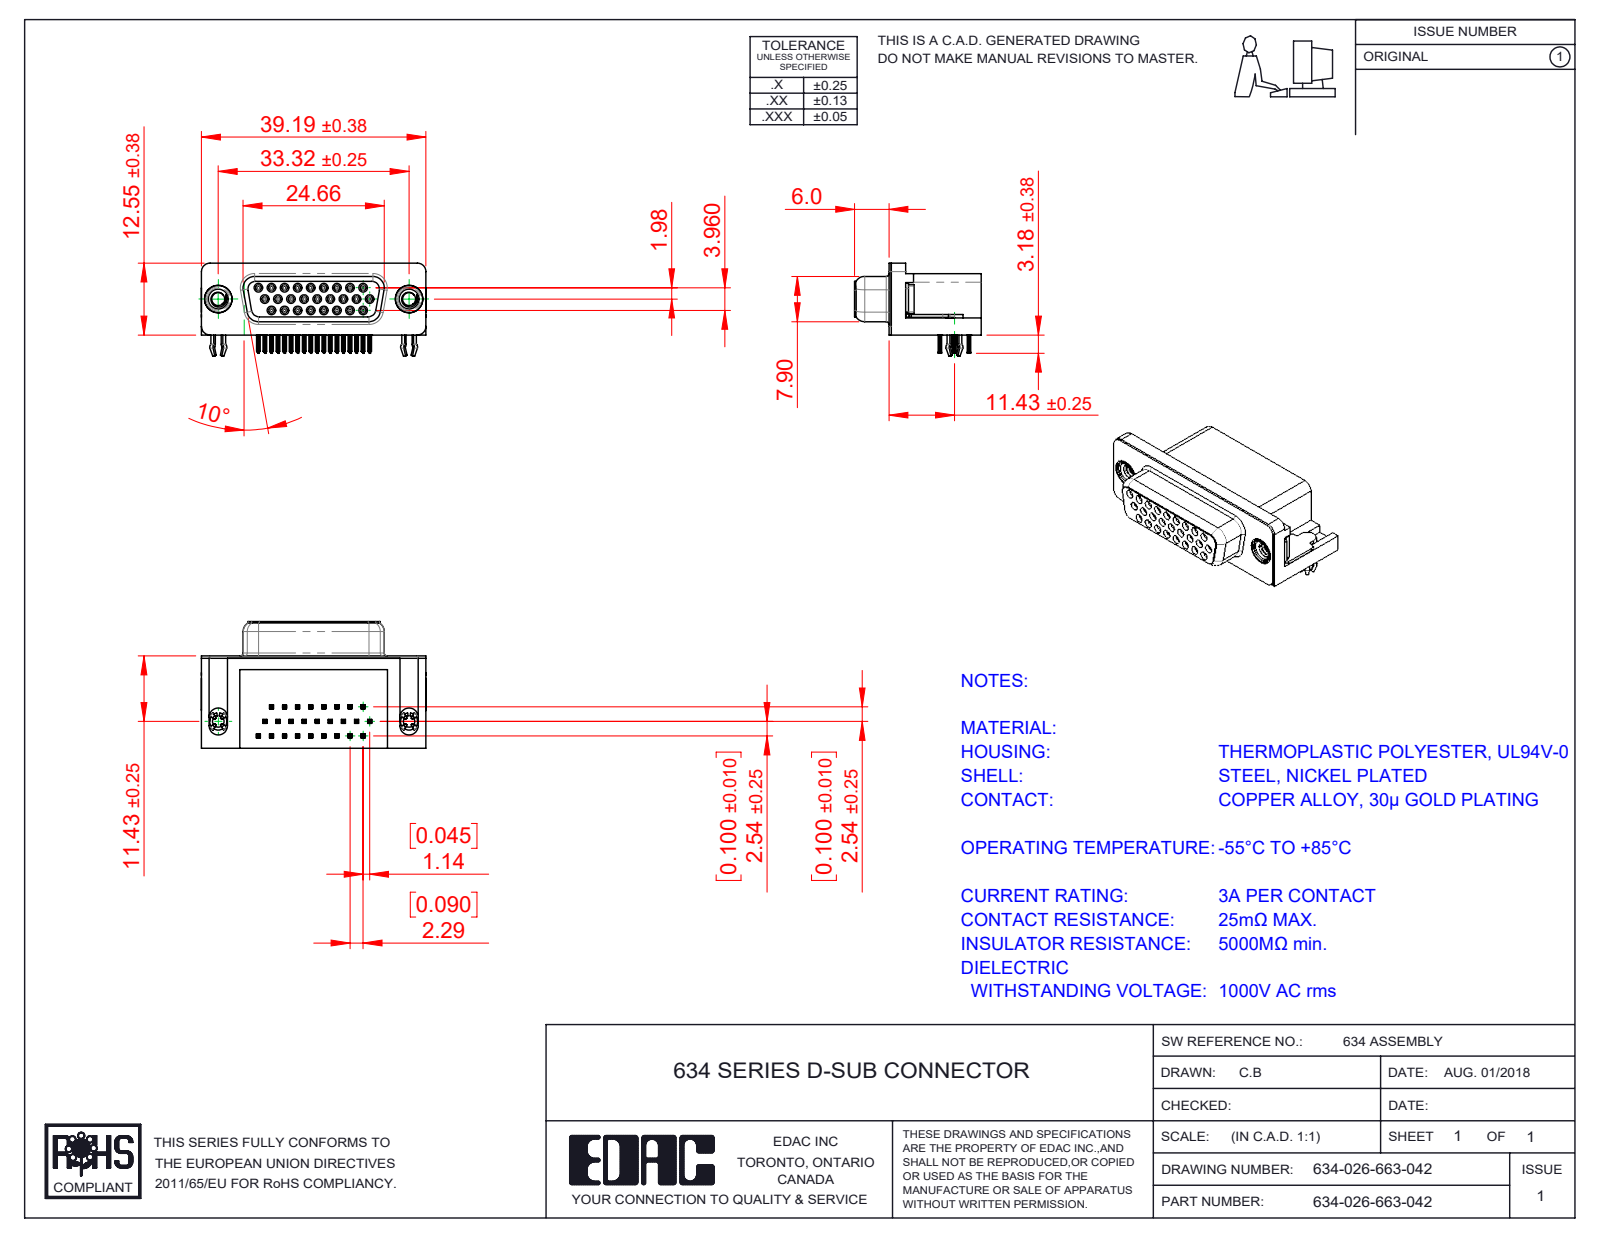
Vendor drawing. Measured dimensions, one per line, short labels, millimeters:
name: Contact Top; 634 Housing_26 Socket; Contact Middle; 634-026-663-042 (+4 more)
written by: SolidWorks 2016 (CONFIG_CONTROL_DESIGN)
unit: mm
bodies: 32 solids, 4101 faces (1813 planar, 944 cylindrical, 1344 other)
size: 39.22 × 22.1 × 16.25
volume: 6 377 mm³; area: 9 154 mm²
holes: 26× ⌀0.8, 26× ⌀0.9, 2× ⌀2, 2× ⌀2.26, 2× ⌀4, 2× ⌀4.8, 2× ⌀5
bosses: 26× ⌀1.2, 2× ⌀4.9, 2× ⌀4.75, 2× ⌀3.9, 2× ⌀3
rounds: 208× R0.1, 104× R0.15, 52× R0.35, 26× R0.34, 19× R1, 12× R0.25, 8× R0.28, 8× R1.35
face distances: 0.4, 10.34, 15.7, 0.35, 16.1, 6.65, 2.5, 0.85, 2.9, 10.69
hole spacings: 2.29, 4.57, 2.28, 3.96, 6.05, 2.3, 2.27, 4.58
